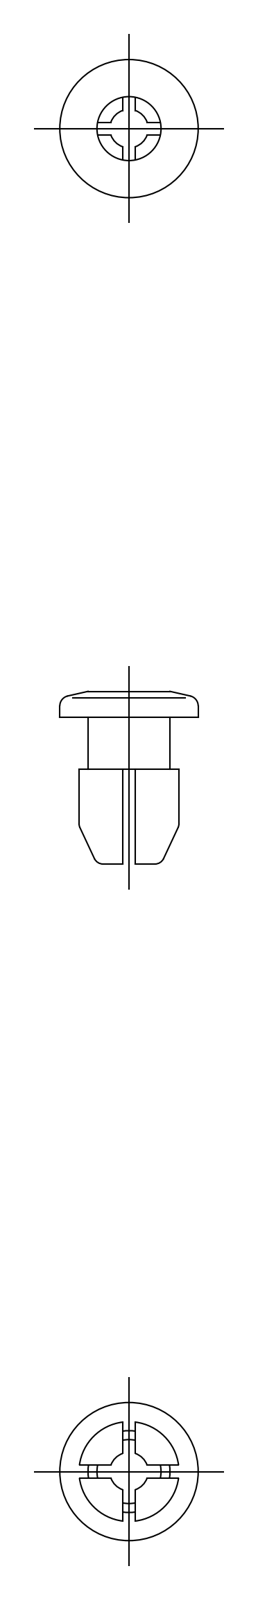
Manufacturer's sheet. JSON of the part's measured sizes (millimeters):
{"part_name": "grommet", "step_written_by": "CADfix (AUTOMOTIVE_DESIGN)", "units": "millimeters", "bodies": {"solids": 1, "faces": 56, "planar": 0, "cylindrical": 0, "other": 56}, "overall_size": [13.5, 10.8, 10.8], "volume_mm3": 328, "surface_area_mm2": 683}
